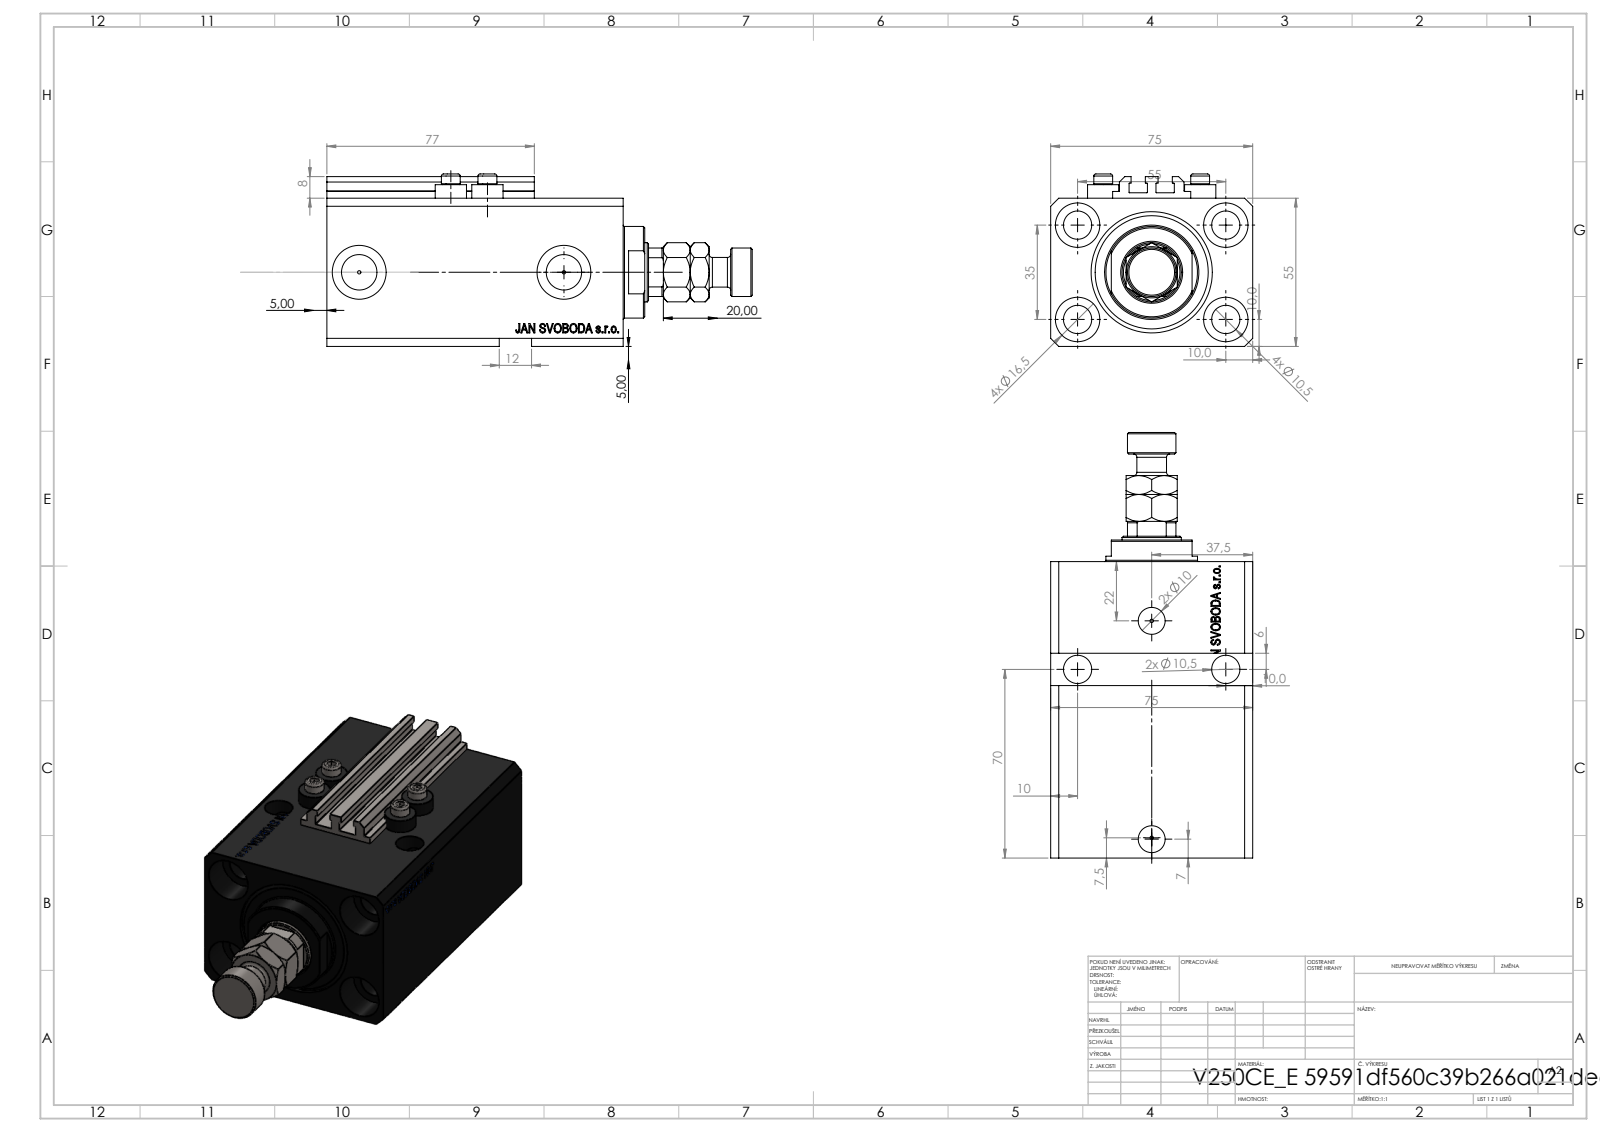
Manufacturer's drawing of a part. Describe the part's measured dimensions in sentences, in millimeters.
The part is named "ALLEN BOLT V250CE; MFA; V250CE_C_VCP; V250CE_VC_E (+1 more)". Its 3-D file was written by "SolidWorks 2019 (CONFIG_CONTROL_DESIGN)". It is 9 solids with 1136 faces: 530 planar, 150 cylindrical and 456 other. Overall it measures 158 by 75 by 64 millimeters. Its volume is 389 405 cubic millimeters and its surface area 98 340 square millimeters. Round holes: 9 of diameter 10.5, 4 of diameter 1.25, 4 of diameter 4, 4 of diameter 16.5, 2 of diameter 10, 2 of diameter 13.16, 2 of diameter 20, 1 of diameter 22, 1 of diameter 32, 1 of diameter 45. Round bosses or shafts: 4 of diameter 11.6, 4 of diameter 7, 1 of diameter 34, 1 of diameter 18, 1 of diameter 11. Partial cylindrical surfaces (rounded edges, fillets, slot ends): 10 of radius 0.2, 1 of radius 10.5. The main face-to-face distances are 55, 75, 15, 110, 95, 3, 9.9, 85.1, 100.1, 2.5. The hole center spacings are 32.6, 32.87, 55, 68.74, 13.6, 14.09, 23.05, 25.81.
